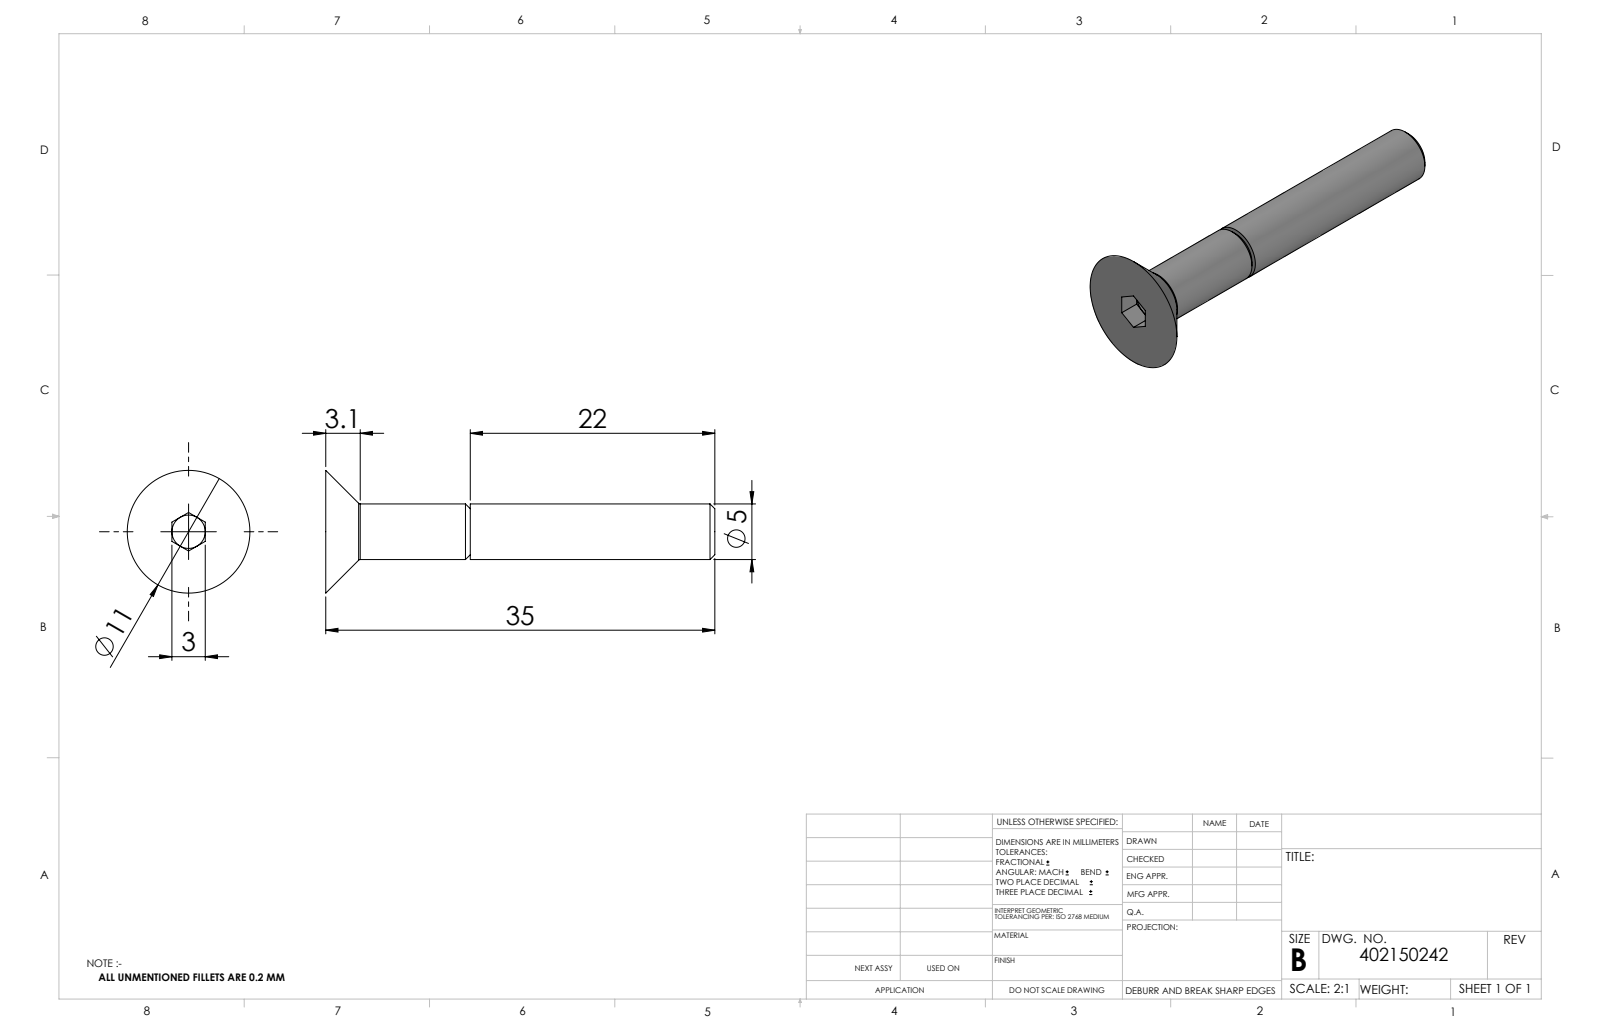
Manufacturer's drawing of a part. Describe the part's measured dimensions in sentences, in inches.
The part is named "402150242_c_1". Its 3-D file was written by "SolidWorks 2014 (CONFIG_CONTROL_DESIGN)". It is 1 solid with 29 faces: 15 planar, 4 cylindrical and 10 other. Overall it measures 1.378 by 0.434 by 0.434 inches. Its volume is 0.047 cubic inches and its surface area 1.16 square inches. Round bosses or shafts: 1 of diameter 0.197. The main face-to-face distances are 1.378, 0.118, 0.512, 0.866, 0.075, 0.437, 1.303.
